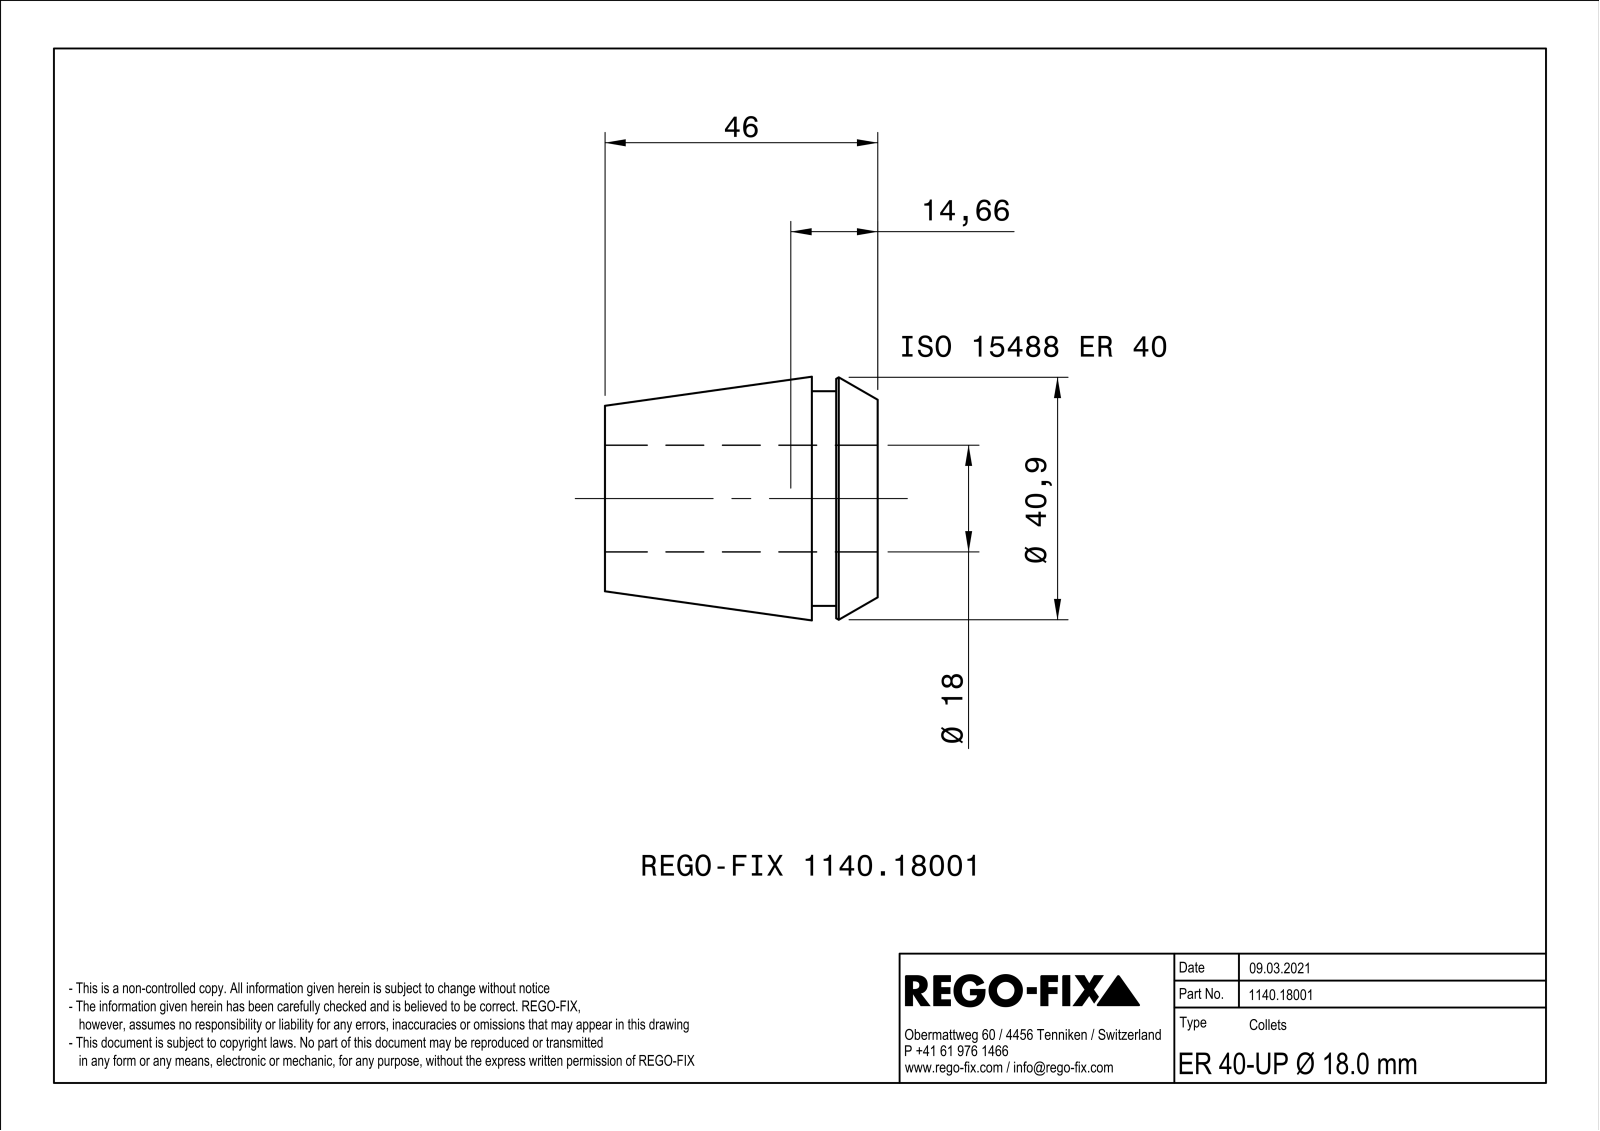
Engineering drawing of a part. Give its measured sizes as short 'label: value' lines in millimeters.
name: NOCUT
written by: SIEMENS PLM Software Solid Edge ST10 (AUTOMOTIVE_DESIGN)
unit: mm
bodies: 1 solid, 177 faces (88 planar, 9 cylindrical, 80 other)
size: 46 × 40.99 × 40.99
volume: 30 165 mm³; area: 20 213 mm²
holes: 1× ⌀18
bosses: 1× ⌀36.2
face distances: 1, 46, 11.1, 34.9, 7, 4.1, 39, 7.5, 0.5, 3.6
